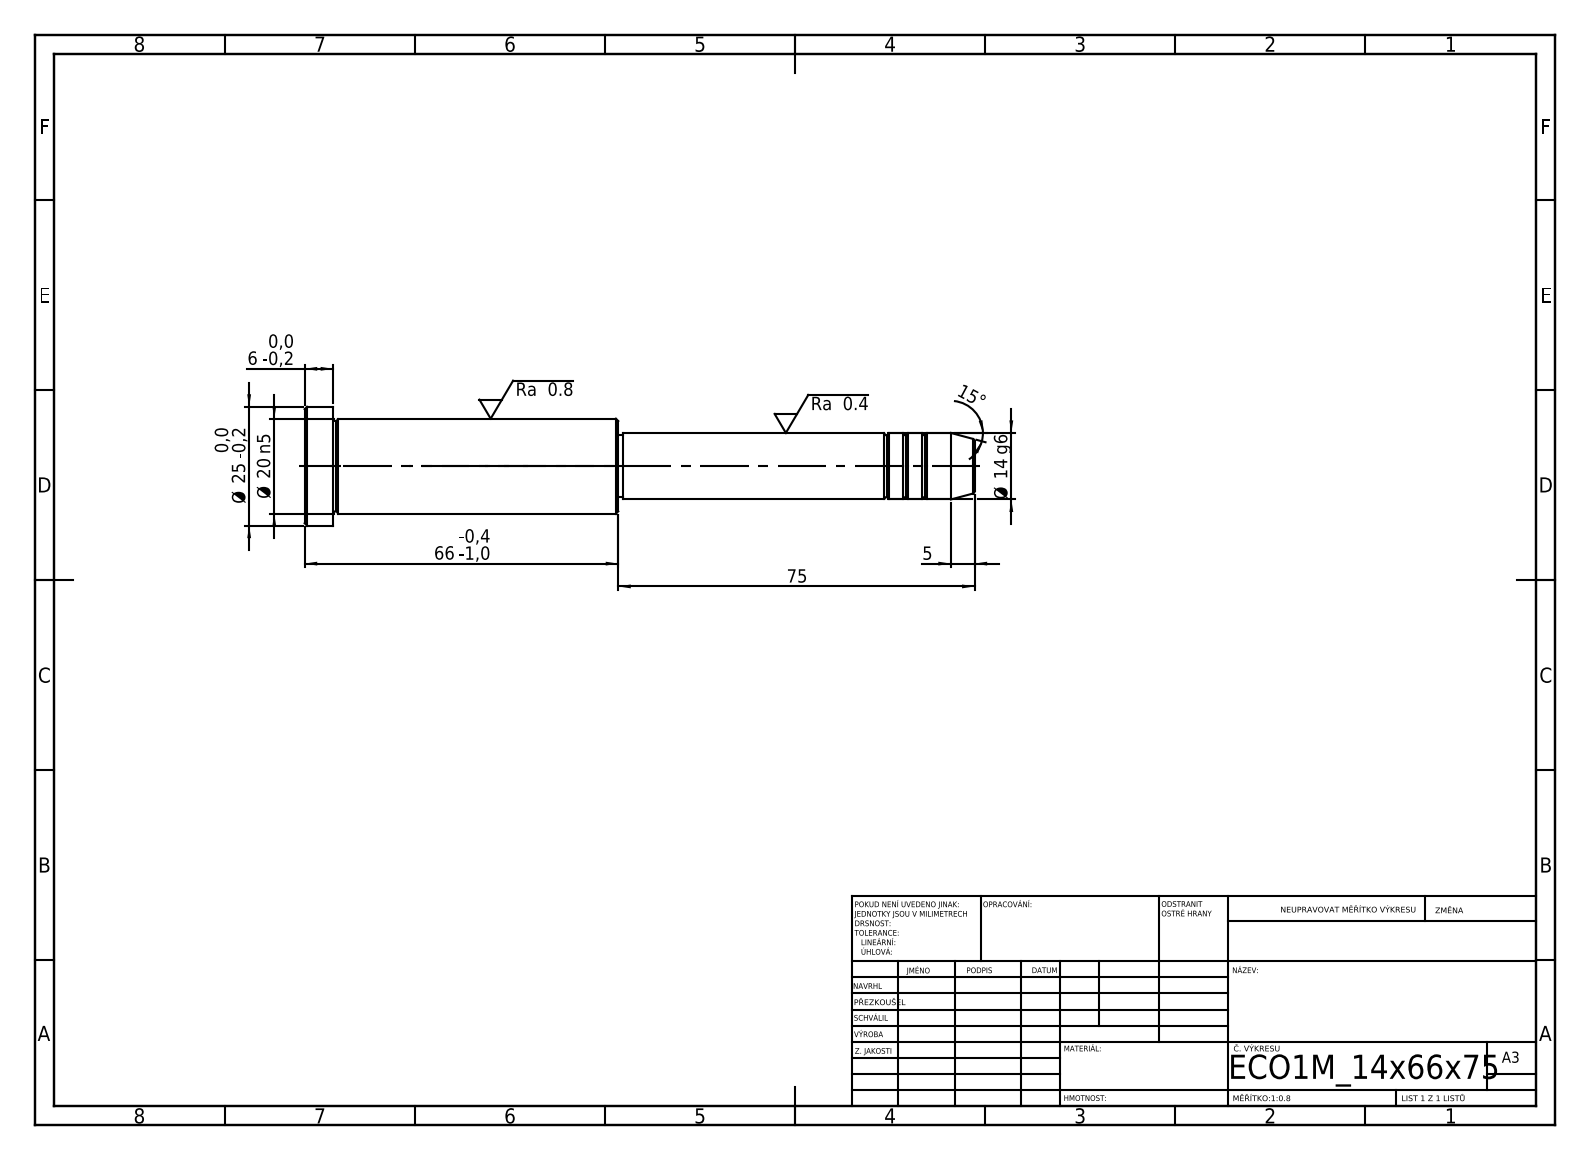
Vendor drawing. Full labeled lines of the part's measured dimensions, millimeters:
STEP written by: SolidWorks 2019 (CONFIG_CONTROL_DESIGN)
Units: millimetres
Bodies: 1 solid, 43 faces (5 planar, 14 cylindrical, 24 other)
Overall size (bounding box): 141 × 25 × 25
Volume: 33 088 mm³ · Surface area: 8 546 mm²
Round bosses / shafts (diameter × count): ⌀25 ×1, ⌀20 ×1, ⌀14 ×1, ⌀13 ×1
Main face-to-face distances: 6, 60, 66, 75, 135, 141, 74, 1, 61, 67
